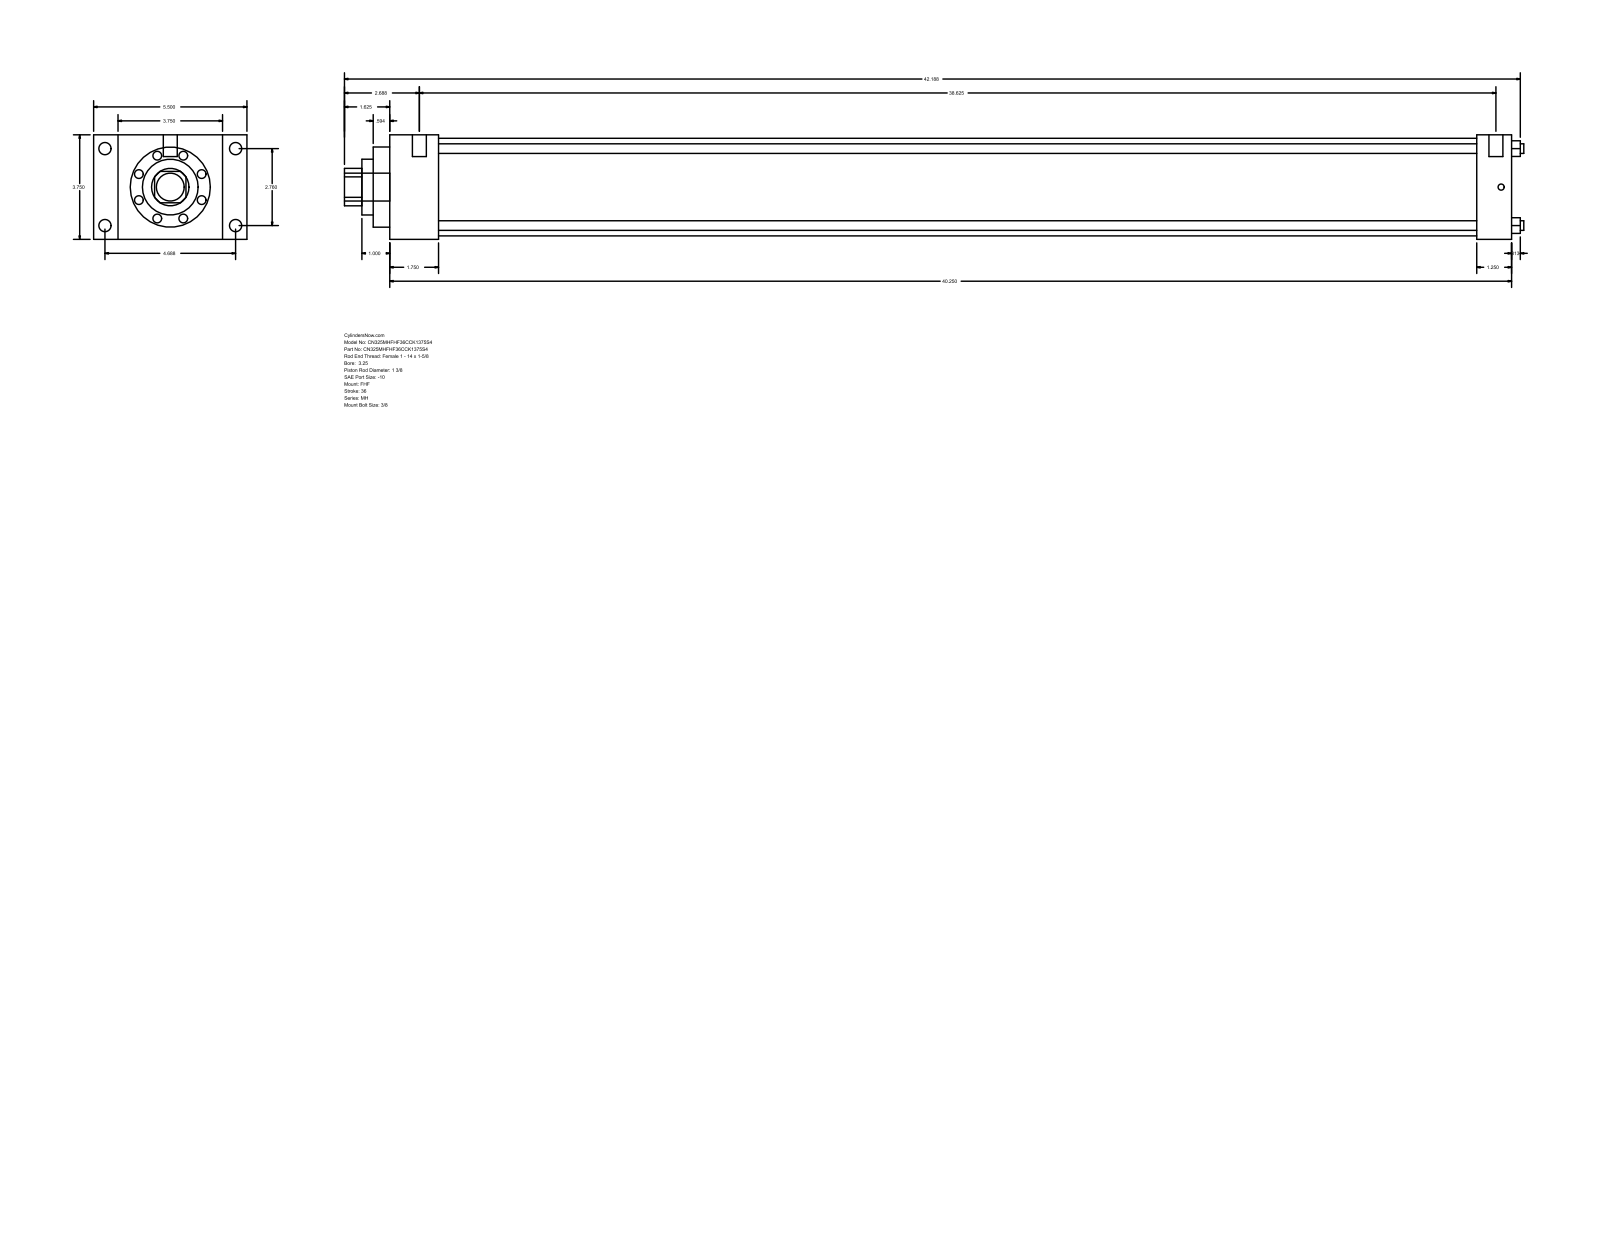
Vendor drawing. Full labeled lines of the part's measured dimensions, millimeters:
Part name (STEP PRODUCT): MH_FHF__0325_1.375
STEP written by: GSSL Pune (CONFIG_CONTROL_DESIGN)
Units: millimetres
Bodies: 0 solids, 90 faces (61 planar, 29 cylindrical, 0 other)
Overall size (bounding box): 1074.74 × 139.7 × 95.25
Round holes (diameter × count): ⌀8.76 ×4, ⌀34.92 ×1, ⌀50.8 ×1, ⌀73.03 ×1, ⌀88.9 ×1
Round bosses / shafts (diameter × count): ⌀11.13 ×4, ⌀5.56 ×4, ⌀12.7 ×2, ⌀25.4 ×1
Partial cylindrical surfaces — rounded edges, fillets, slot ends (radius × count): R17.06 ×1
Main face-to-face distances: 95.24, 1022.35, 44.45, 977.9, 22.23, 117.47, 139.7, 990.61, 946.16, 31.74
Hole centre spacings: 49.57, 70.1, 99.14
